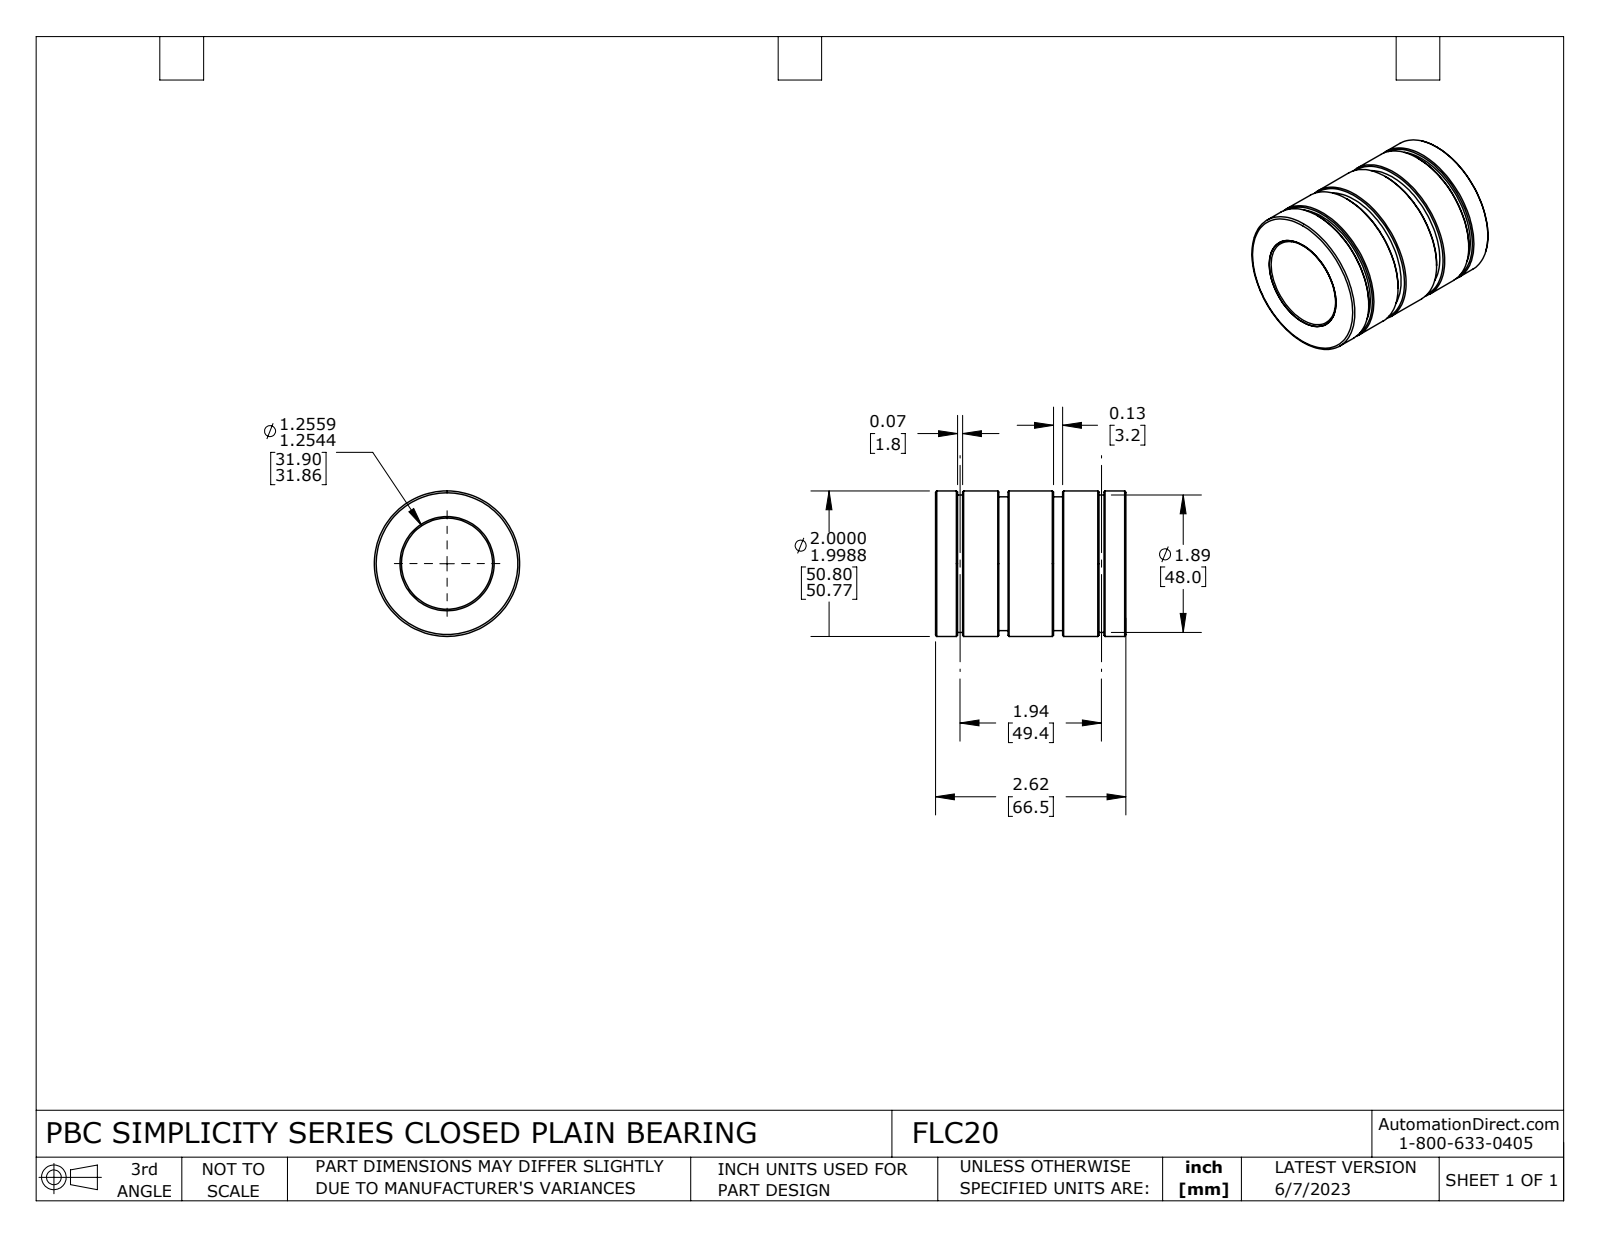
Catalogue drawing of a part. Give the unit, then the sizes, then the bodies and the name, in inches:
Units: inches
Overall size (bounding box): 2.617 × 1.999 × 1.999
Round holes (diameter × count): ⌀1.252 ×1, ⌀1.295 ×1
Round bosses / shafts (diameter × count): ⌀1.999 ×1, ⌀1.889 ×1, ⌀1.838 ×1
Main face-to-face distances: 2.617, 0.996, 1.621, 0.87, 1.747, 0.126, 0.751, 0.302, 2.316, 0.569
Volume: 4.818 in³ · Surface area: 54.29 in²
Bodies: 2 solids, 58 faces (10 planar, 24 cylindrical, 24 other)
Part name (STEP PRODUCT): FLC20
STEP written by: SolidWorks 2021 (CONFIG_CONTROL_DESIGN)
